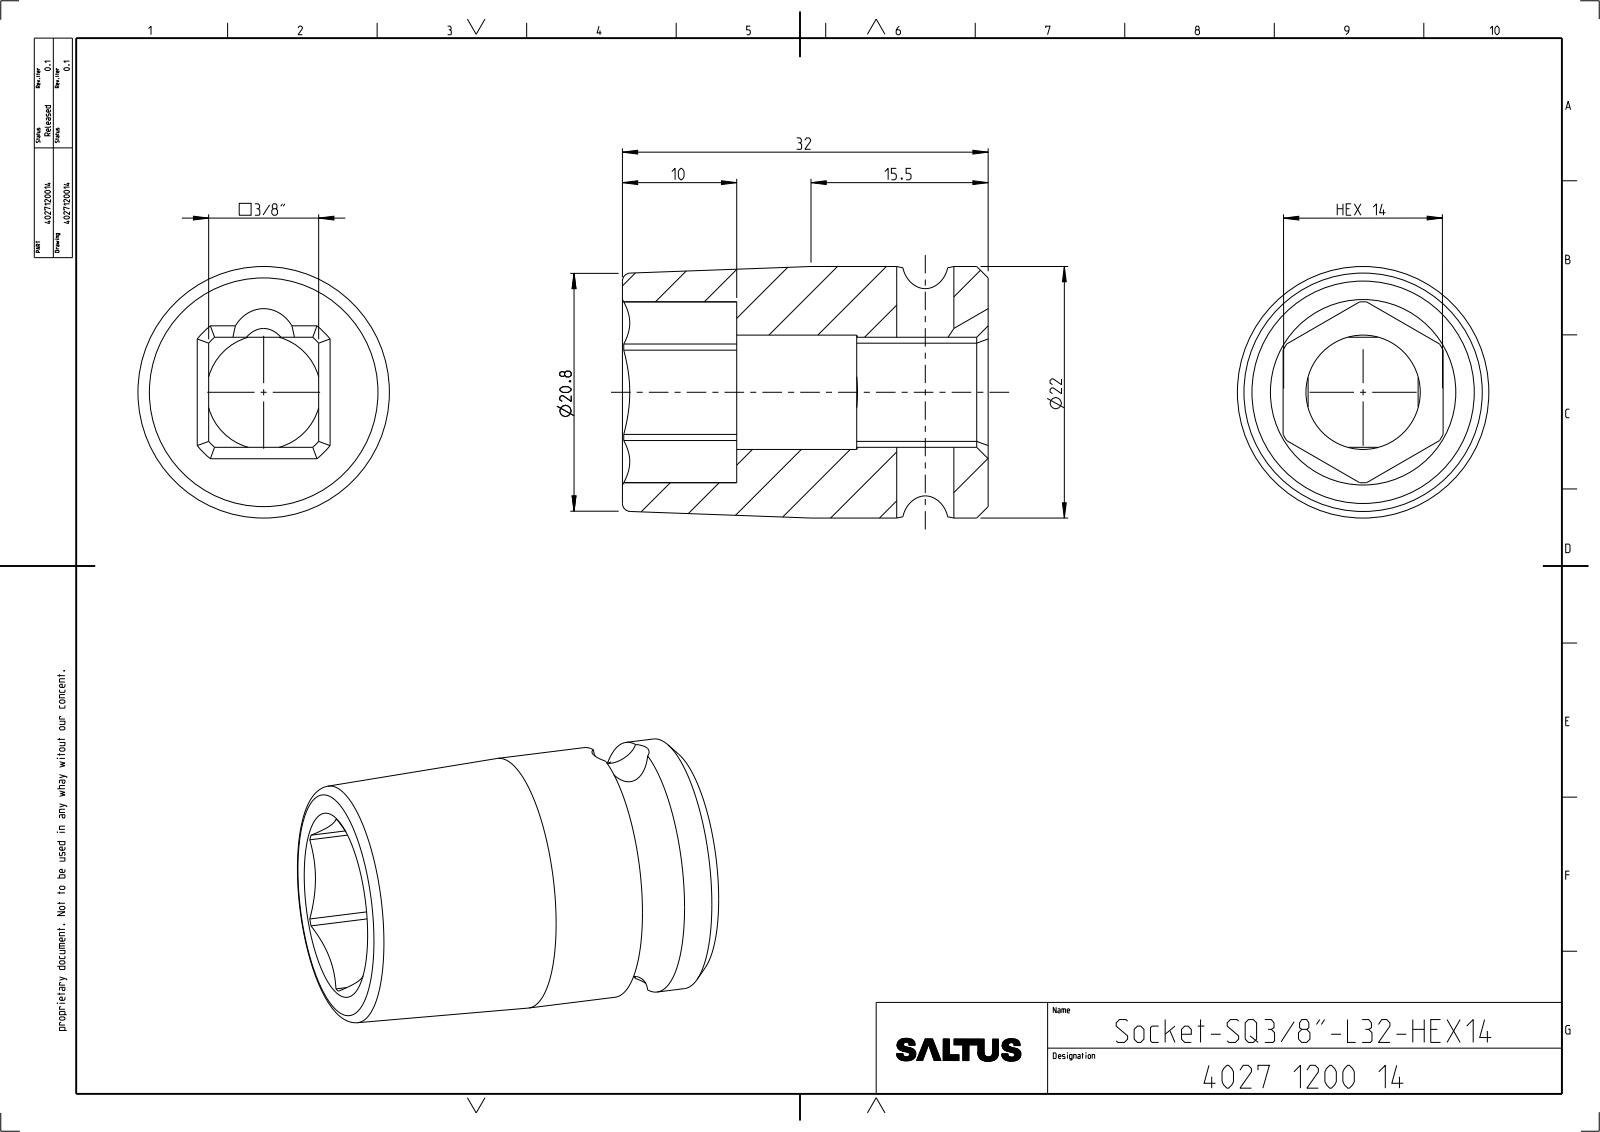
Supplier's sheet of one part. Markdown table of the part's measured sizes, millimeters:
| quantity | value |
| --- | --- |
| part name | 4027120014 |
| STEP written by | CREO PARAMETRIC BY PTC INC, 2022414 (CONFIG_CONTROL_DESIGN) |
| units | millimeters |
| bodies | 1 solid, 61 faces (22 planar, 21 cylindrical, 18 other) |
| overall size | 32 × 22 × 22 |
| volume | 7 664 mm³ |
| surface area | 4 036 mm² |
| round holes (diameter × count) | 5 × 1, 10 × 1 |
| round bosses / shafts (diameter × count) | 22 × 1 |
| partial cylindrical surfaces (radius × count) | 3 × 1, 6.45 × 1, 7.91 × 1 |
| main face-to-face distances | 14, 9.62, 2.19, 11.81, 22, 32, 10, 11.5, 10.5, 20.5 |
